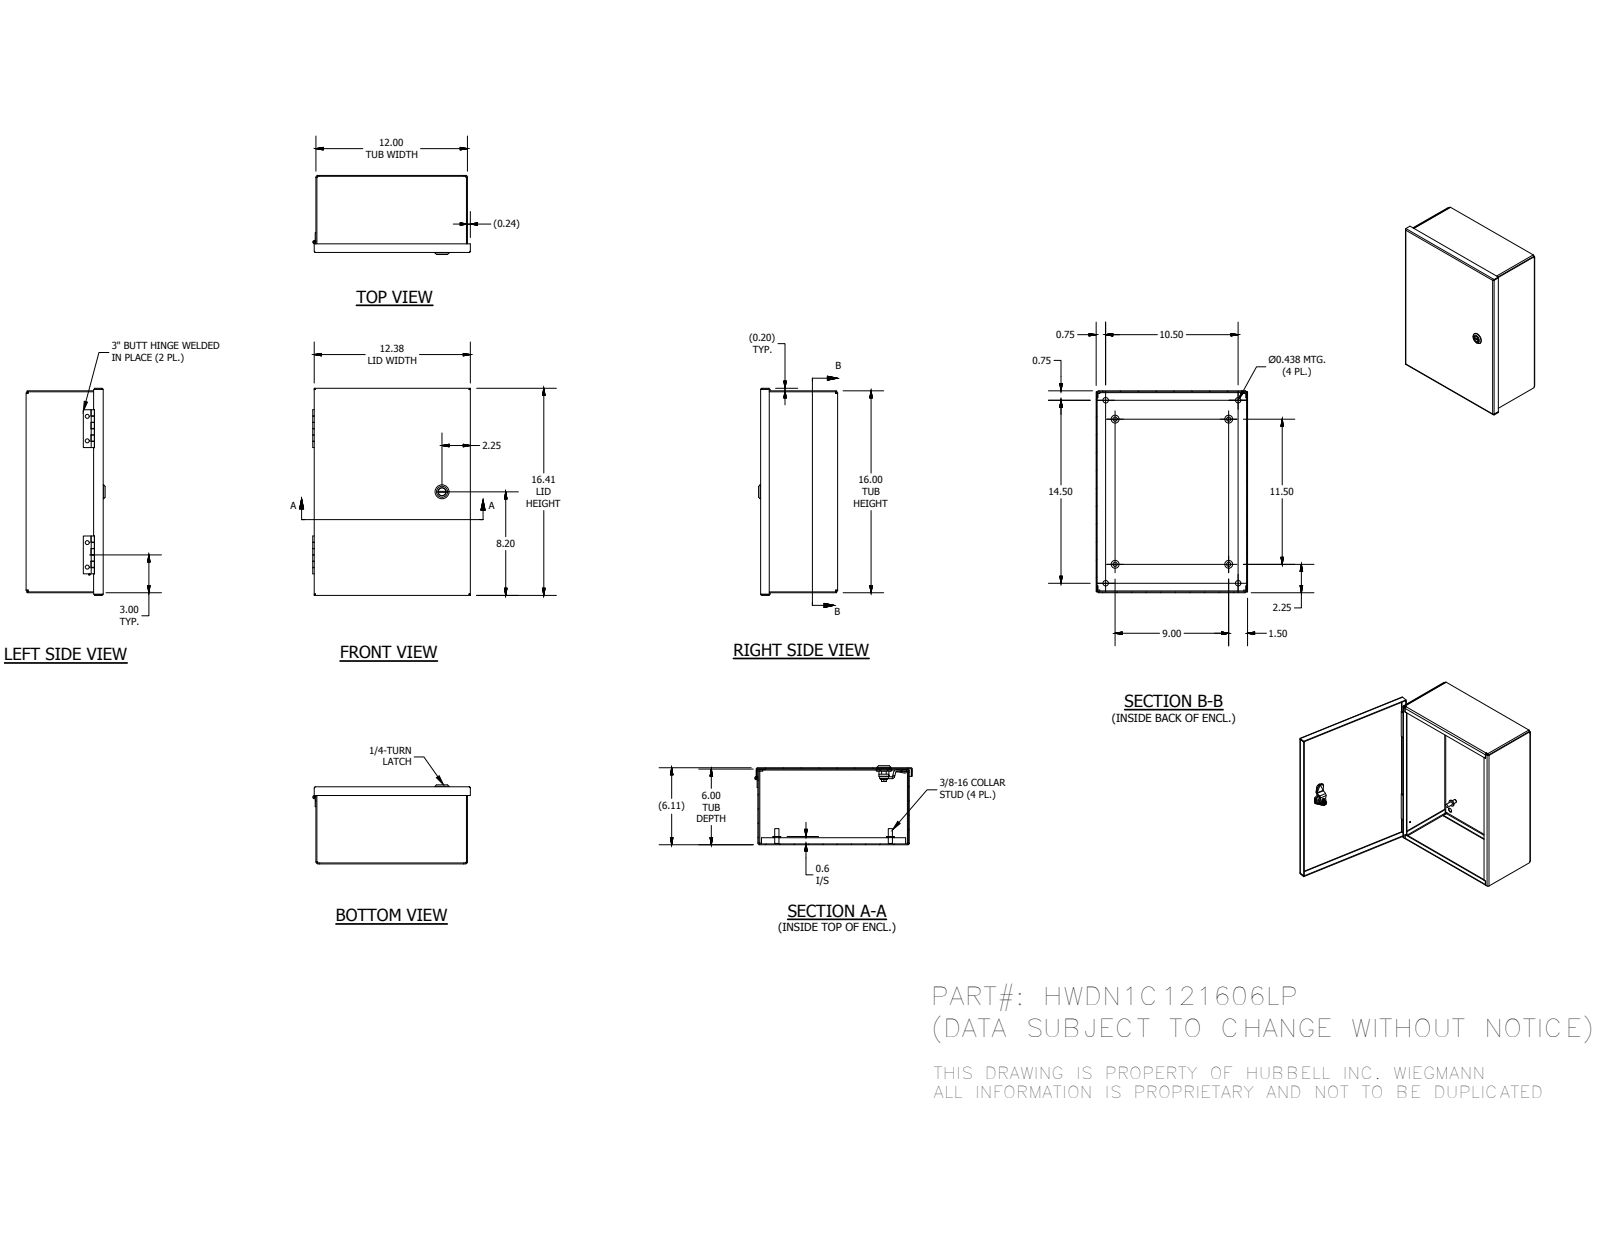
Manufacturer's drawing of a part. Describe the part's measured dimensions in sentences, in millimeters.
The part is named "N1C121606LPBLR; N1C1206LPTB; N1C1216LPLID; 1000-101-GPF_GPD (+8 more)". Its 3-D file was written by "Autodesk Inventor 2016 (AUTOMOTIVE_DESIGN)". It is 21 solids with 717 faces: 437 planar, 212 cylindrical and 68 other. Overall it measures 416.72 by 317.21 by 178.12 millimeters. Its volume is 1 051 000 cubic millimeters and its surface area 1 127 000 square millimeters. Round holes: 4 of diameter 7.95, 4 of diameter 11.11, 1 of diameter 3.05, 1 of diameter 3.3, 1 of diameter 5, 1 of diameter 8, 1 of diameter 10, 1 of diameter 10.2, 1 of diameter 16.1, 1 of diameter 20.38. Round bosses or shafts: 4 of diameter 15.88, 4 of diameter 8.38, 1 of diameter 28, 1 of diameter 27, 1 of diameter 23, 1 of diameter 19.8, 1 of diameter 15.8, 1 of diameter 15.2. Partial cylindrical surfaces (rounded edges, fillets, slot ends): 30 of radius 0.3, 12 of radius 3.47, 10 of radius 0.5, 10 of radius 1.59, 4 of radius 0.79, 4 of radius 2.67, 4 of radius 4, 3 of radius 0.4. The main face-to-face distances are 1.88, 172.24, 302.92, 170.36, 174.12, 404.52, 301.04, 304.8, 402.64, 406.4. The hole center spacings are 49.28, 186.92, 254, 266.7, 298.29, 368.3, 454.72, 15.51.
